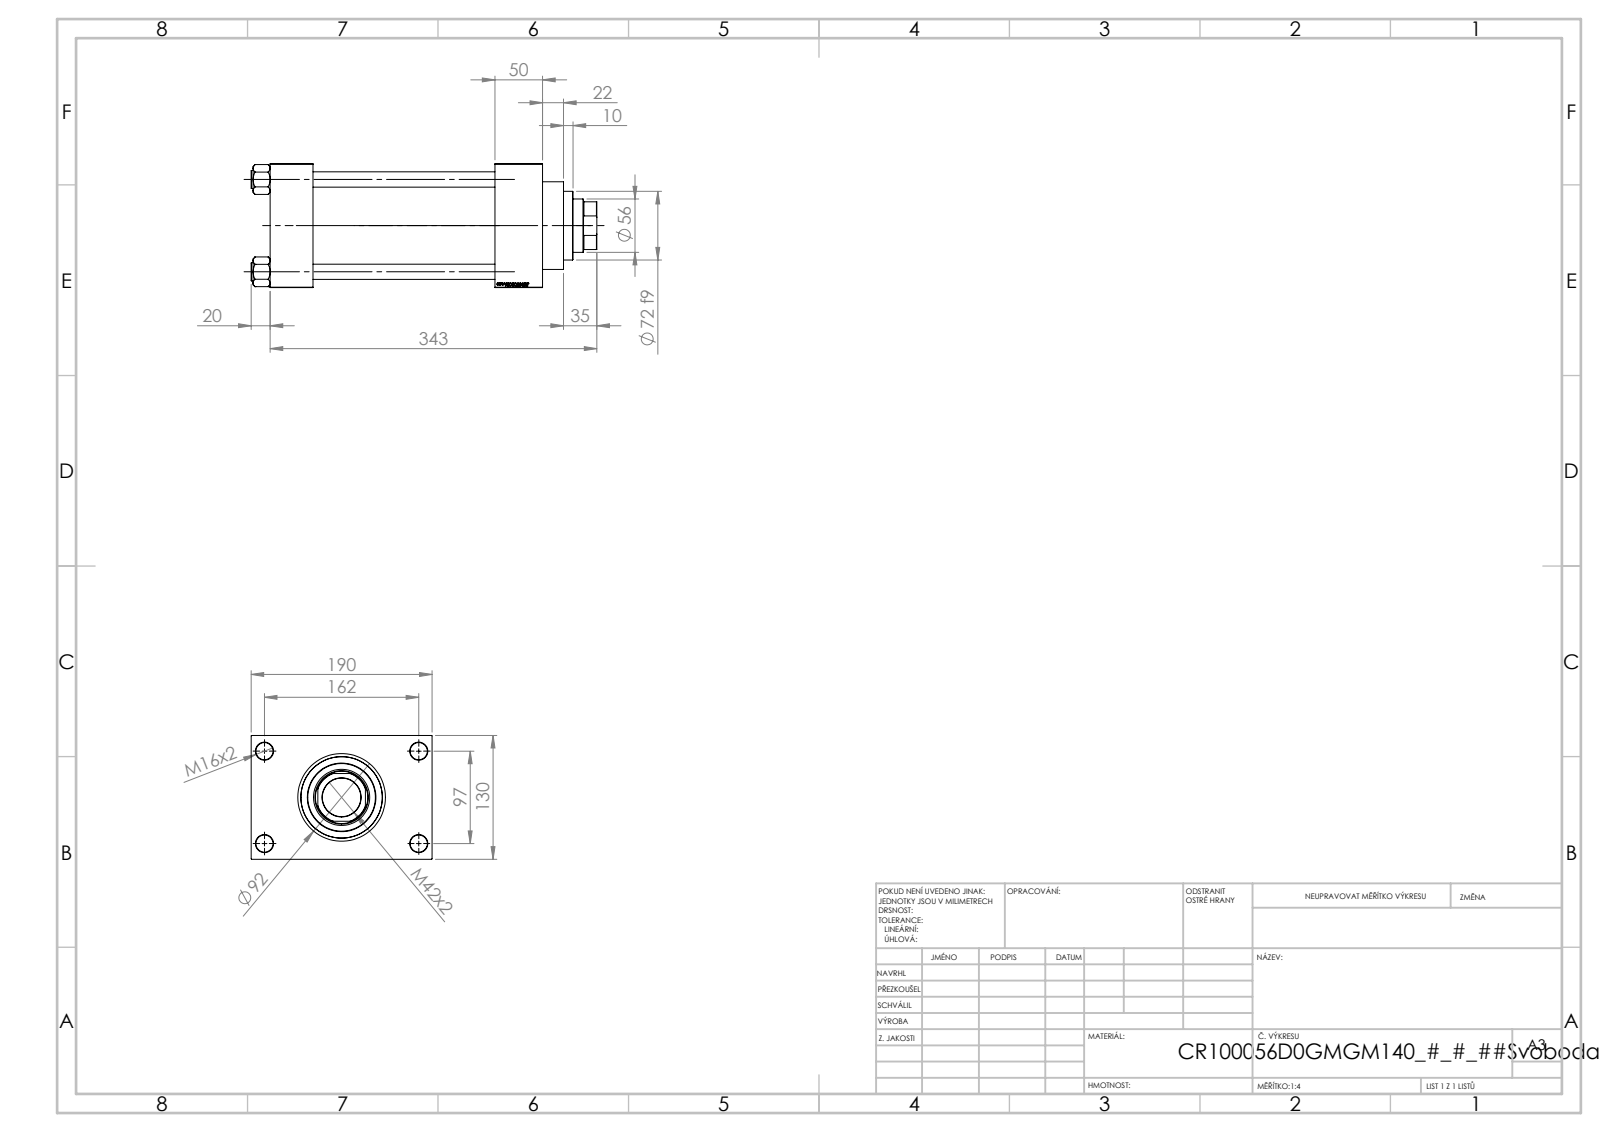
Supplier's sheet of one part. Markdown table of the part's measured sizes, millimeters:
| quantity | value |
| --- | --- |
| part name | V215CR_VCP_D; V215CR_D_Body; NUT_M5_D; V215CR_D_TYCINKA (+1 more) |
| STEP written by | SolidWorks 2019 (CONFIG_CONTROL_DESIGN) |
| units | millimeters |
| bodies | 11 solids, 1151 faces (545 planar, 88 cylindrical, 518 other) |
| overall size | 363 × 190 × 130 |
| volume | 3 137 000 mm³ |
| surface area | 485 121 mm² |
| round holes (diameter × count) | 16 × 4, 18 × 4, 7 × 2, 26.44 × 2, 35 × 2, 40.5 × 1, 56 × 1, 59 × 1, 76 × 1, 85.5 × 1, 100 × 1 |
| round bosses / shafts (diameter × count) | 19 × 4, 106 × 1, 92 × 1, 72 × 1 |
| partial cylindrical surfaces (radius × count) | 27 × 1 |
| main face-to-face distances | 130, 50, 45, 236, 191, 286, 241, 30, 190, 160 |
| hole center spacings | 32.55, 68.52, 94.41, 96.9, 102.27, 129.45, 161.73, 97 |
